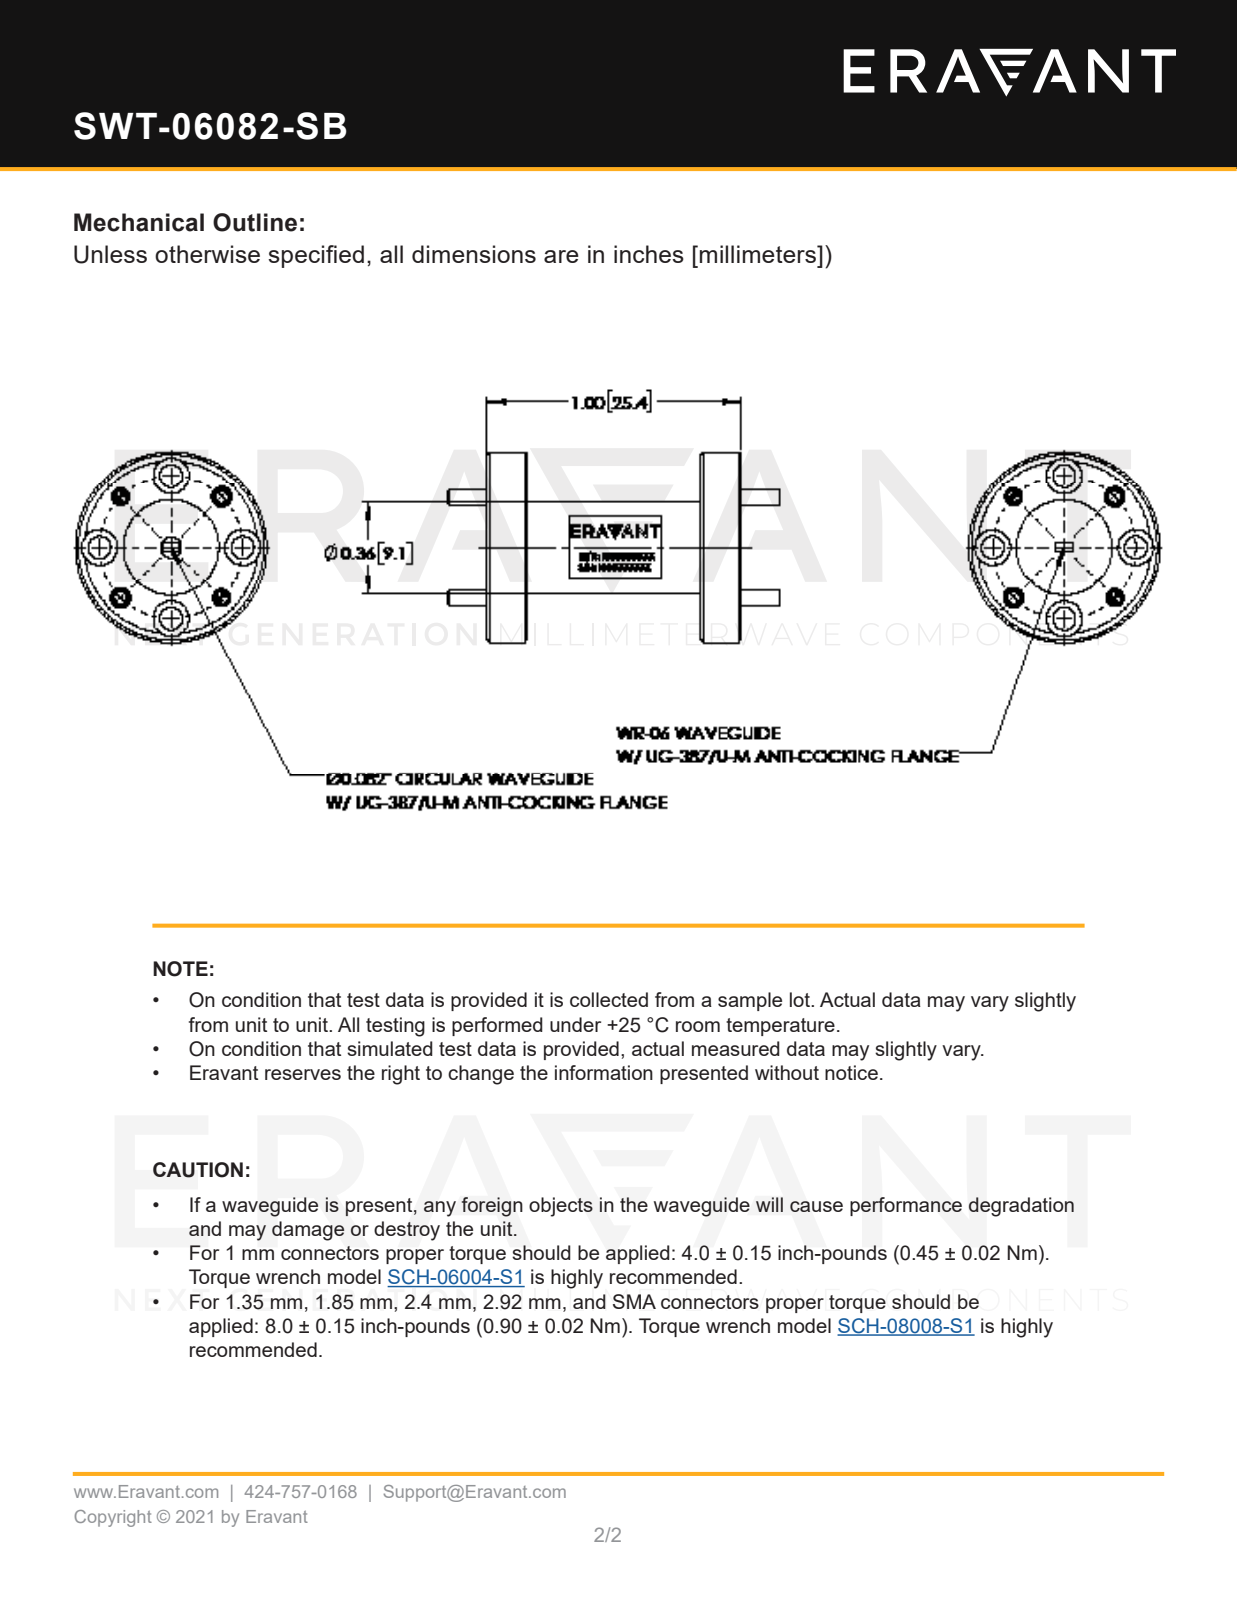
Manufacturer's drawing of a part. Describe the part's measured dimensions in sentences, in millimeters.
The part is named "SWT-06082-SB". Its 3-D file was written by "SolidWorks 2021 (CONFIG_CONTROL_DESIGN)". It is 5 solids with 148 faces: 26 planar, 74 cylindrical and 48 other. Overall it measures 33.1 by 19.1 by 19.1 millimeters. Its volume is 3 110 cubic millimeters and its surface area 2 495 square millimeters. Round holes: 4 of diameter 1.5, 4 of diameter 1.7, 4 of diameter 2.3, 4 of diameter 3.6, 1 of diameter 17.3. Round bosses or shafts: 4 of diameter 1.6, 1 of diameter 19.1, 1 of diameter 9.5, 1 of diameter 9.5, 1 of diameter 9.1. The main face-to-face distances are 24.9, 0.5, 17.3, 20.8, 3.6, 3.6, 20.8, 24.4, 21.3, 4.1. The hole center spacings are 5.5, 10.1, 7.1, 13.2, 14.3, 13.2, 7.1, 14.3.
